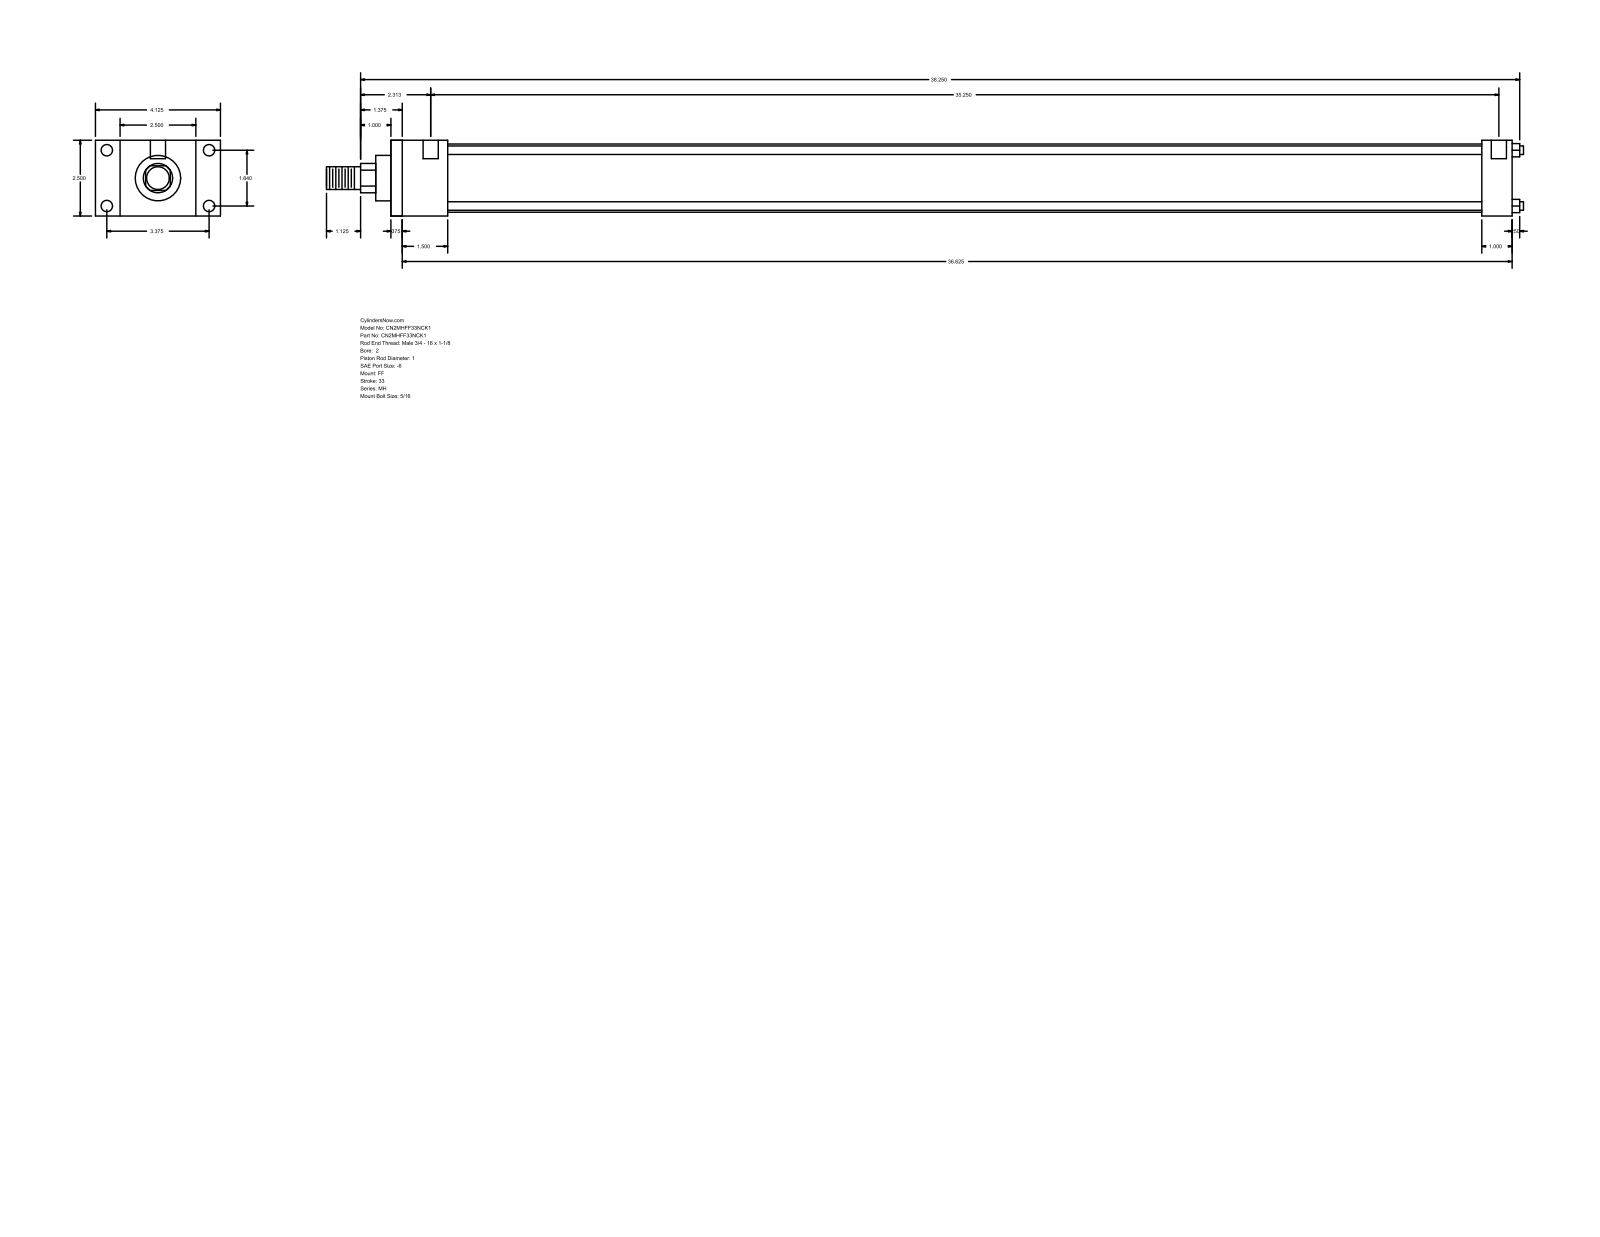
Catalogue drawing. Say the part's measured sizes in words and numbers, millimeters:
The part is named "MH_FF__0200_1". Its 3-D file was written by "GSSL Pune (CONFIG_CONTROL_DESIGN)". It is 0 solids with 92 faces: 64 planar, 28 cylindrical and 0 other. Overall it measures 1003.3 by 104.78 by 63.5 millimeters. Round holes: 4 of diameter 5.56, 4 of diameter 9.53, 2 of diameter 12.7. Round bosses or shafts: 4 of diameter 7.14, 1 of diameter 57.15, 1 of diameter 38.1, 1 of diameter 25.4, 1 of diameter 19.05. Partial cylindrical surfaces (rounded edges, fillets, slot ends): 1 of radius 12.29. The main face-to-face distances are 63.5, 939.8, 9.52, 930.28, 20.64, 25.4, 47.63, 914.4, 38.11, 904.88. The hole center spacings are 46.74, 85.72, 97.63, 903.28, 3.17, 4.76, 895.35, 898.52.
